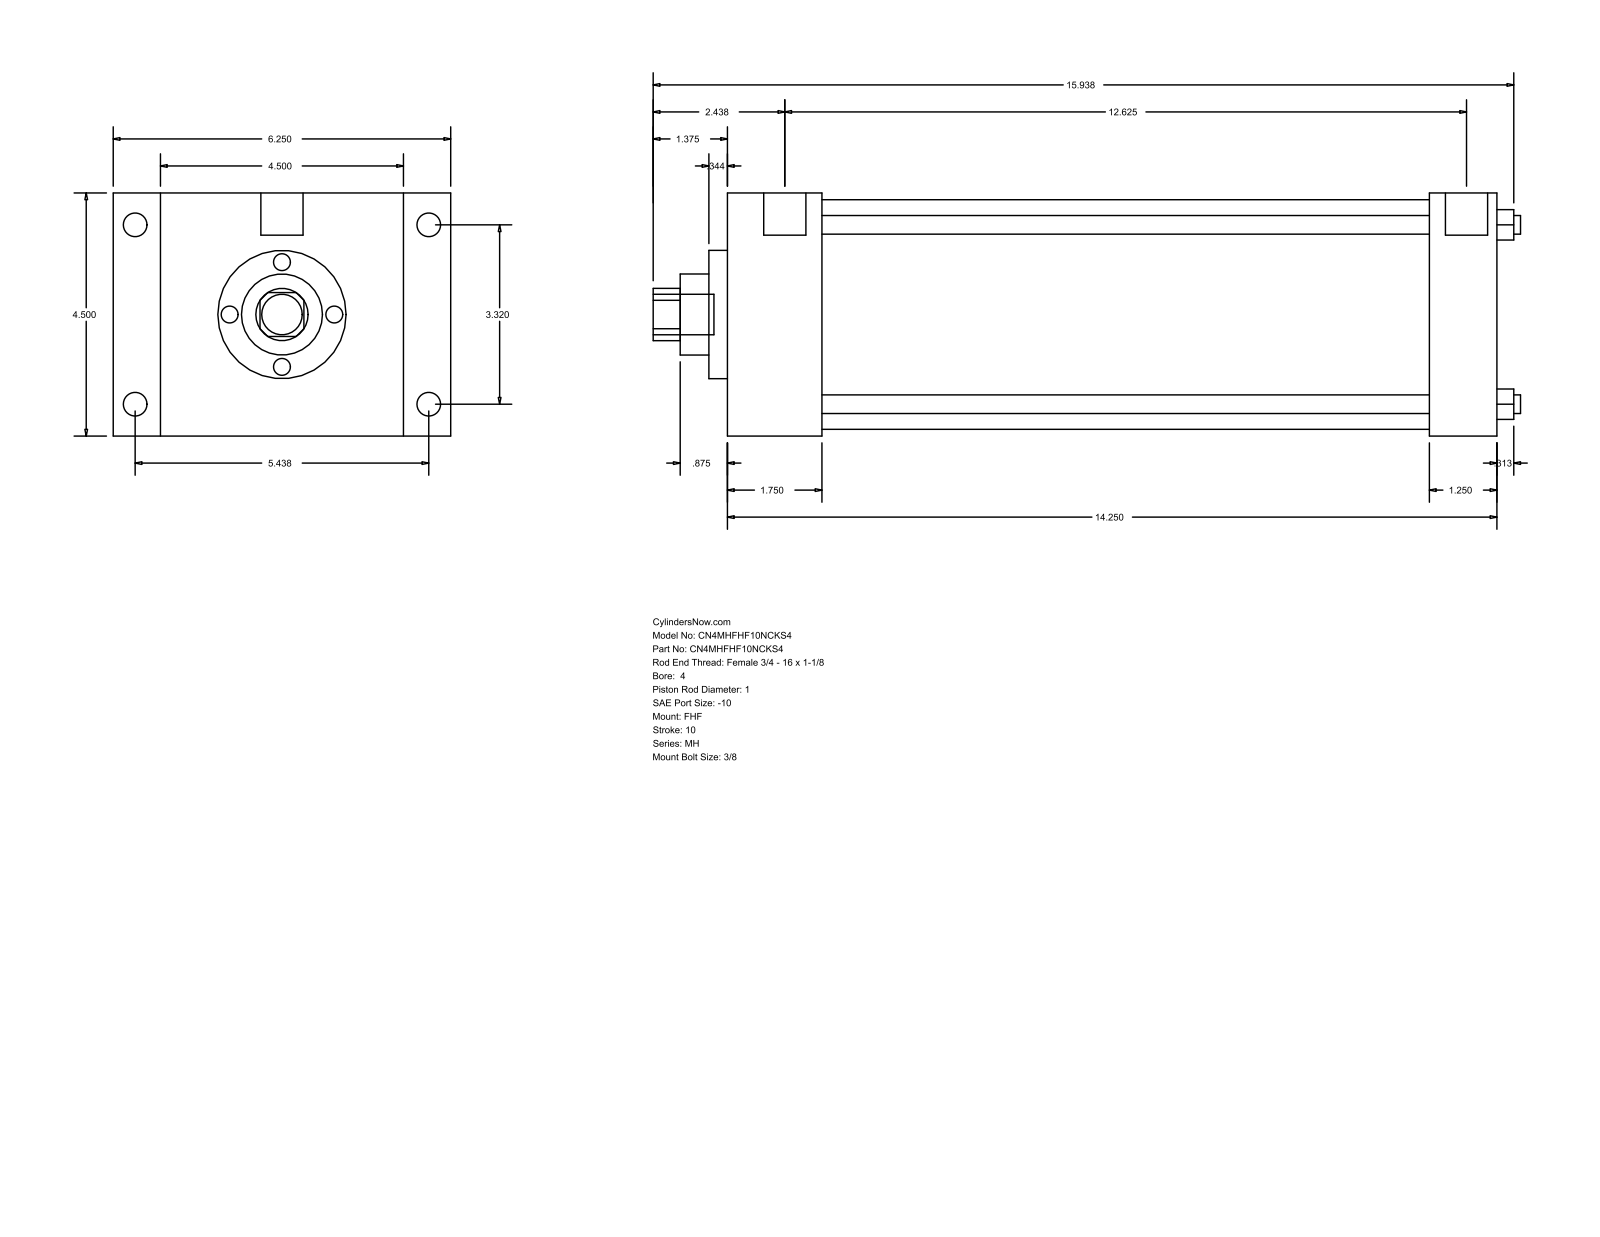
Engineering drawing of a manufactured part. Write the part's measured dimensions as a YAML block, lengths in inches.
part_name: "MH_FHF__0400_1"
step_written_by: "GSSL Pune (CONFIG_CONTROL_DESIGN)"
units: inches
bodies: {solids: 0, faces: 90, planar: 61, cylindrical: 29, other: 0}
overall_size: [16.063, 6.25, 4.5]
round_holes:
  - {diameter: 0.345, count: 4}
  - {diameter: 1, count: 1}
  - {diameter: 1.5, count: 1}
  - {diameter: 2.375, count: 1}
  - {diameter: 4.25, count: 1}
round_bosses_or_shafts:
  - {diameter: 0.438, count: 4}
  - {diameter: 0.344, count: 4}
  - {diameter: 0.781, count: 2}
  - {diameter: 0.75, count: 1}
partial_cylinders:
  - {radius: 0.484, count: 1}
face_to_face_distances: [4.5, 14.25, 1.75, 12.5, 0.875, 5.375, 6.25, 13, 11.25, 1.25]
hole_center_spacings: [2.347, 3.32, 4.695]
